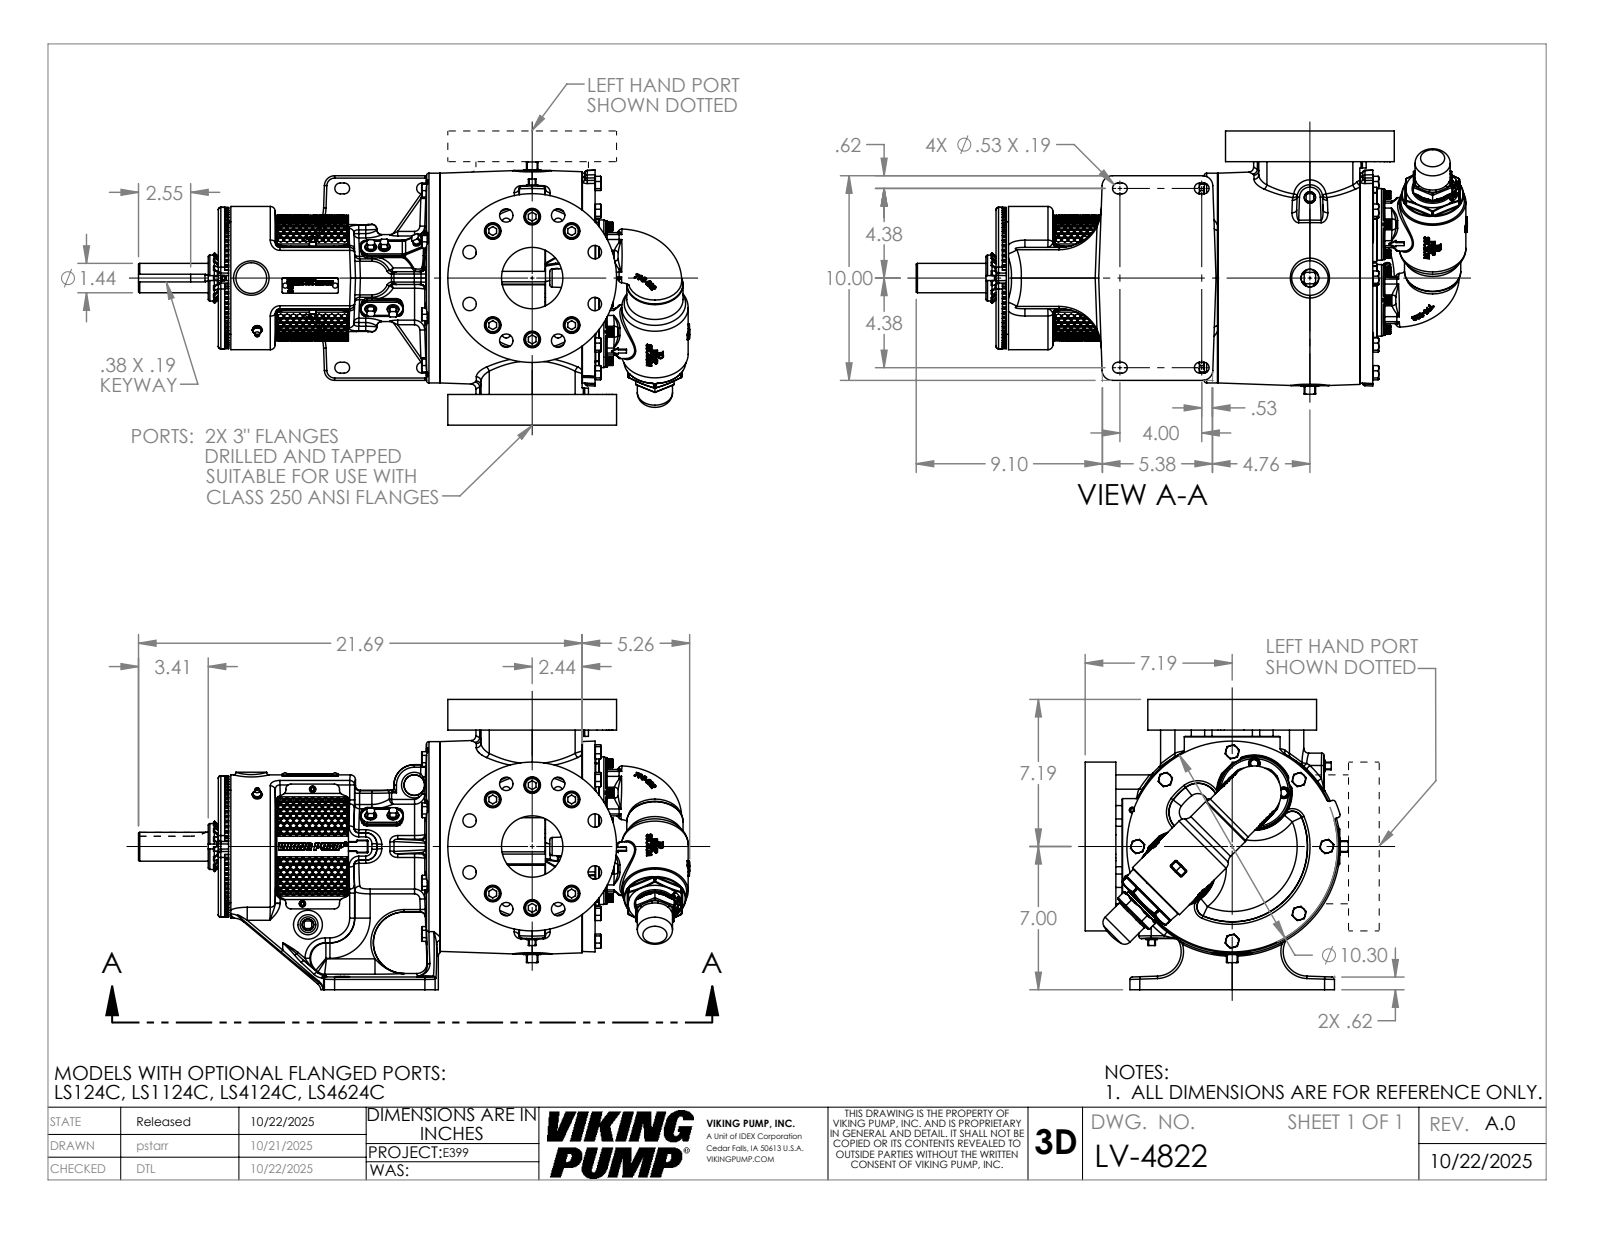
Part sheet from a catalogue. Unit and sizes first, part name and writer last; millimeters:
Units: millimetres
Overall size (bounding box): 684.39 × 360.36 × 326.71
Round holes (diameter × count): ⌀16.67 ×16, ⌀20.62 ×12, ⌀6.35 ×9, ⌀27.79 ×8, ⌀5.05 ×6, ⌀4.04 ×3, ⌀6.76 ×2, ⌀7.94 ×2, ⌀76.2 ×2, ⌀11.51 ×1, ⌀38.25 ×1, ⌀39.42 ×1
Round bosses / shafts (diameter × count): ⌀19.05 ×12, ⌀15.88 ×10, ⌀14.29 ×8, ⌀15.87 ×6, ⌀88.9 ×3, ⌀7.92 ×3, ⌀4.83 ×3, ⌀209.55 ×2
Partial cylindrical surfaces — rounded edges, fillets, slot ends (radius × count): R1.61 ×109, R3.05 ×78, R1.75 ×74, R6.1 ×48, R0.76 ×38, R11.43 ×16, R25.4 ×16, R12.7 ×14
Main face-to-face distances: 38.1, 360.36, 322.26, 12.7, 308.06, 89.94, 398, 57.15, 35.1, 3
Hole centre spacings: 76.2, 84.14, 118.99, 155.46, 34.93, 25.62, 32.24, 38.88
Volume: 19 850 000 mm³ · Surface area: 1 046 000 mm²
Bodies: 1 solid, 5974 faces (2044 planar, 1174 cylindrical, 2756 other)
Part name (STEP PRODUCT): LV-4822
STEP written by: SolidWorks 2024 (AUTOMOTIVE_DESIGN)
